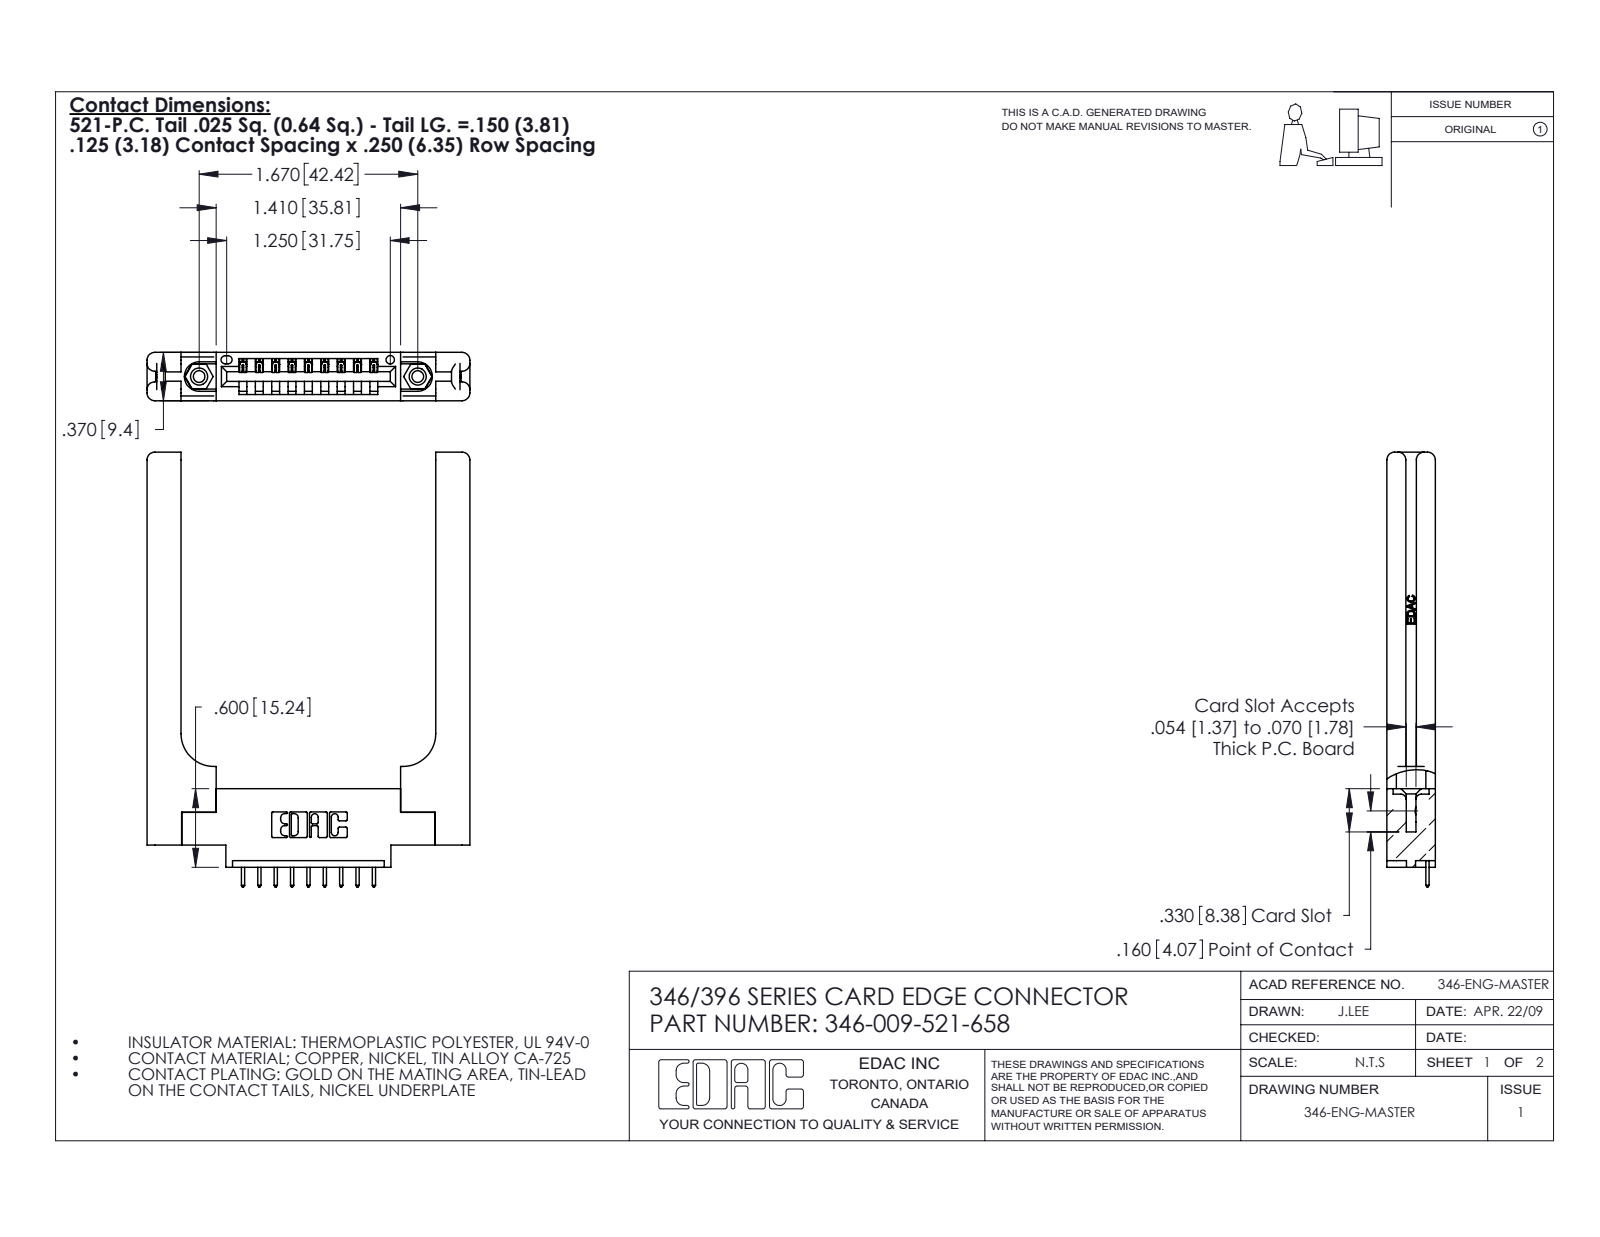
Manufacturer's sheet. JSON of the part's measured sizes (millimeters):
{"part_name": "345-250-001_345-250-001-102; 346 Part_0.170 Offset - 0.156 Dia-TH; 346-009-521-658; 346-220-058_345-220-058 (+1 more)", "step_written_by": "SolidWorks 2020 (CONFIG_CONTROL_DESIGN)", "units": "millimeters", "bodies": {"solids": 14, "faces": 918, "planar": 602, "cylindrical": 256, "other": 60}, "overall_size": [84.3, 62.6, 9.4], "volume_mm3": 13100, "surface_area_mm2": 11860, "round_holes": [[2.3, 2], [3.2, 2], [4, 2], [1.6, 1]], "round_bosses_or_shafts": [[3.9, 2]], "partial_cylinders_radius": [[0.3, 22], [0.2, 18], [0.3, 18], [1.5, 16], [0.2, 6], [0.8, 6], [0.7, 3], [0.8, 2]], "face_to_face_distances": [9.4, 3.8, 5.6, 1.8, 3.8, 6.4, 1.2, 8.2, 2.6, 4.4], "hole_center_spacings": [6.2, 37.2, 42.4]}
